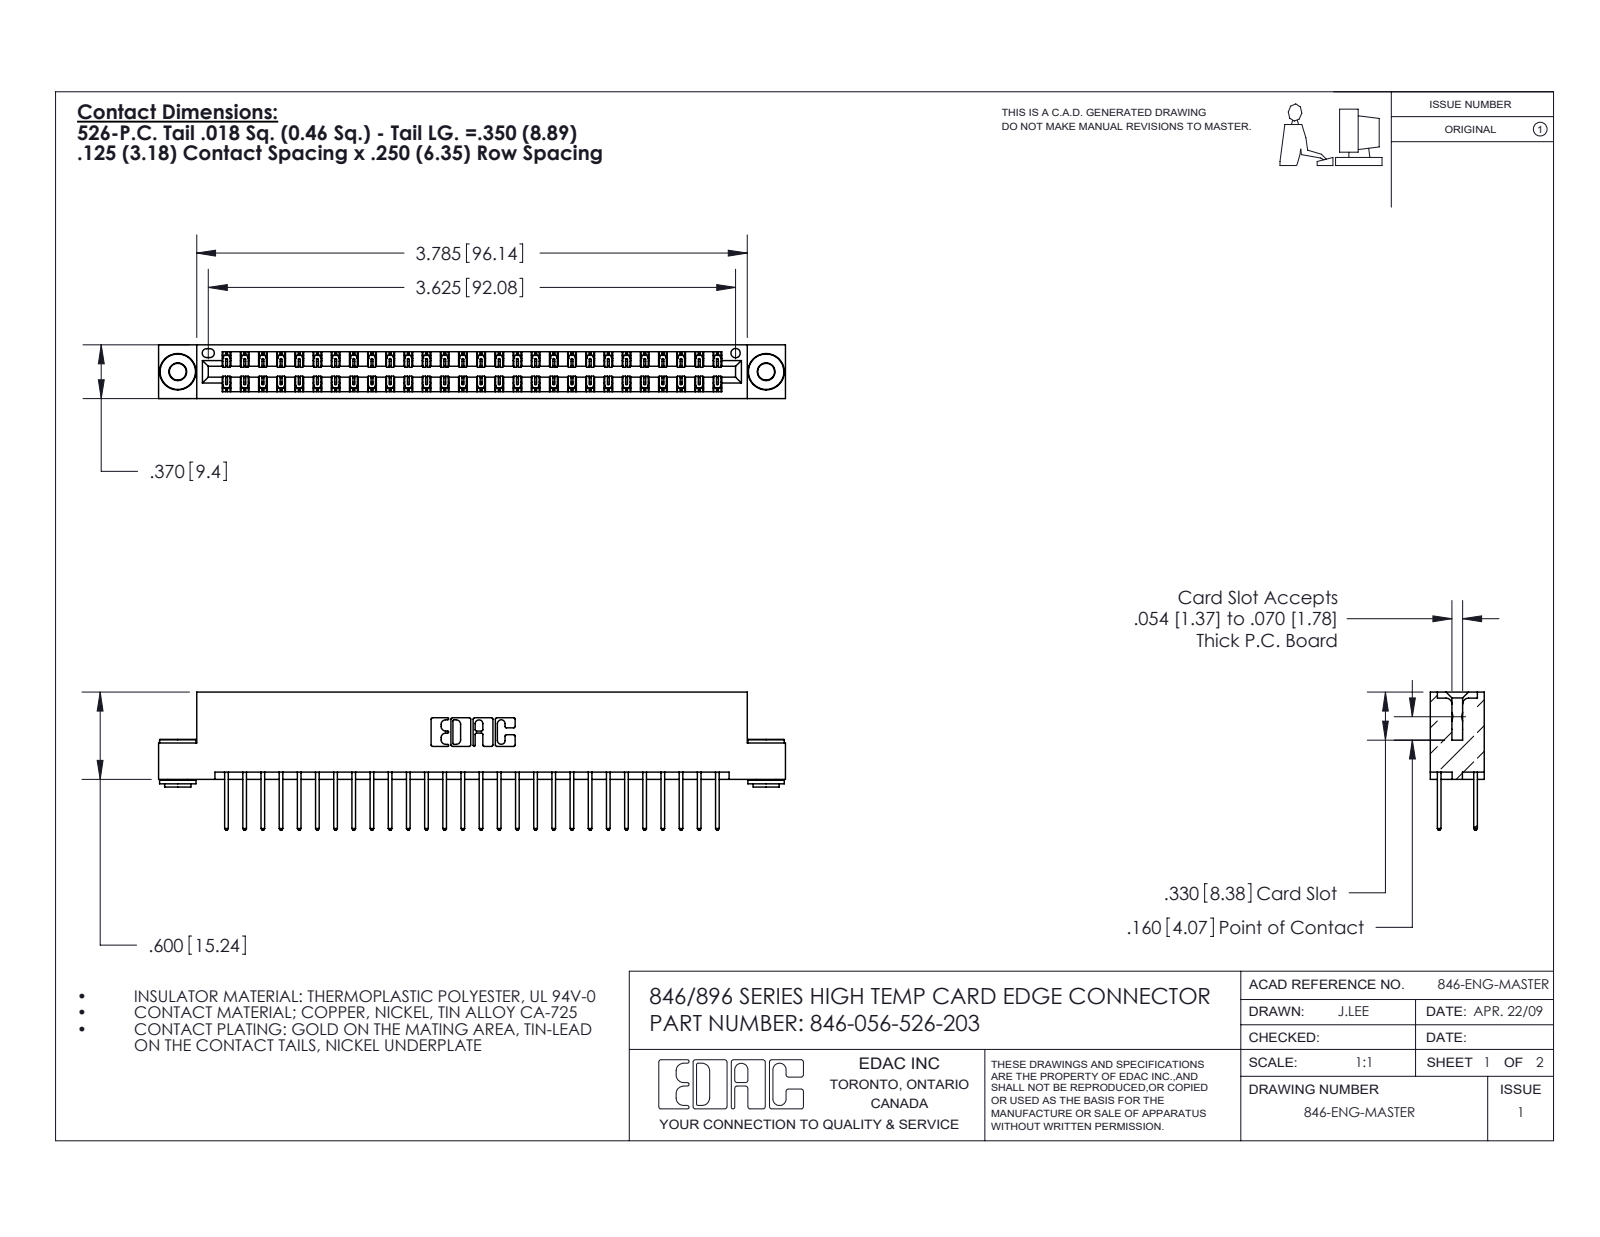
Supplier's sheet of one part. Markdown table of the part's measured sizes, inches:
| quantity | value |
| --- | --- |
| part name | 345-250-002_345-250-002-102; 345-292-001_345-293-126; 346 Part_Flush Mounting Lugs - 0.156 Dia-TH; 346-056-526-203 |
| STEP written by | SolidWorks 2016 (CONFIG_CONTROL_DESIGN) |
| units | inches |
| bodies | 59 solids, 3072 faces (2046 planar, 1018 cylindrical, 8 other) |
| overall size | 4.31 × 0.95 × 0.37 |
| volume | 0.652 in³ |
| surface area | 23.38 in² |
| round holes (diameter × count) | 0.116 × 2, 0.156 × 2, 0.064 × 1 |
| round bosses / shafts (diameter × count) | 0.25 × 2, 0.18 × 2, 0.136 × 2 |
| partial cylindrical surfaces (radius × count) | 0.006 × 84, 0.01 × 56, 0.01 × 22, 0.007 × 6, 0.031 × 6, 0.026 × 3, 0.014 × 2, 0.022 × 2 |
| main face-to-face distances | 0.048, 0.322, 0.25, 0.37, 0.025, 0.072, 0.298, 0.275, 0.148, 0.222 |
| hole center spacings | 0.246, 3.837, 4.045 |
